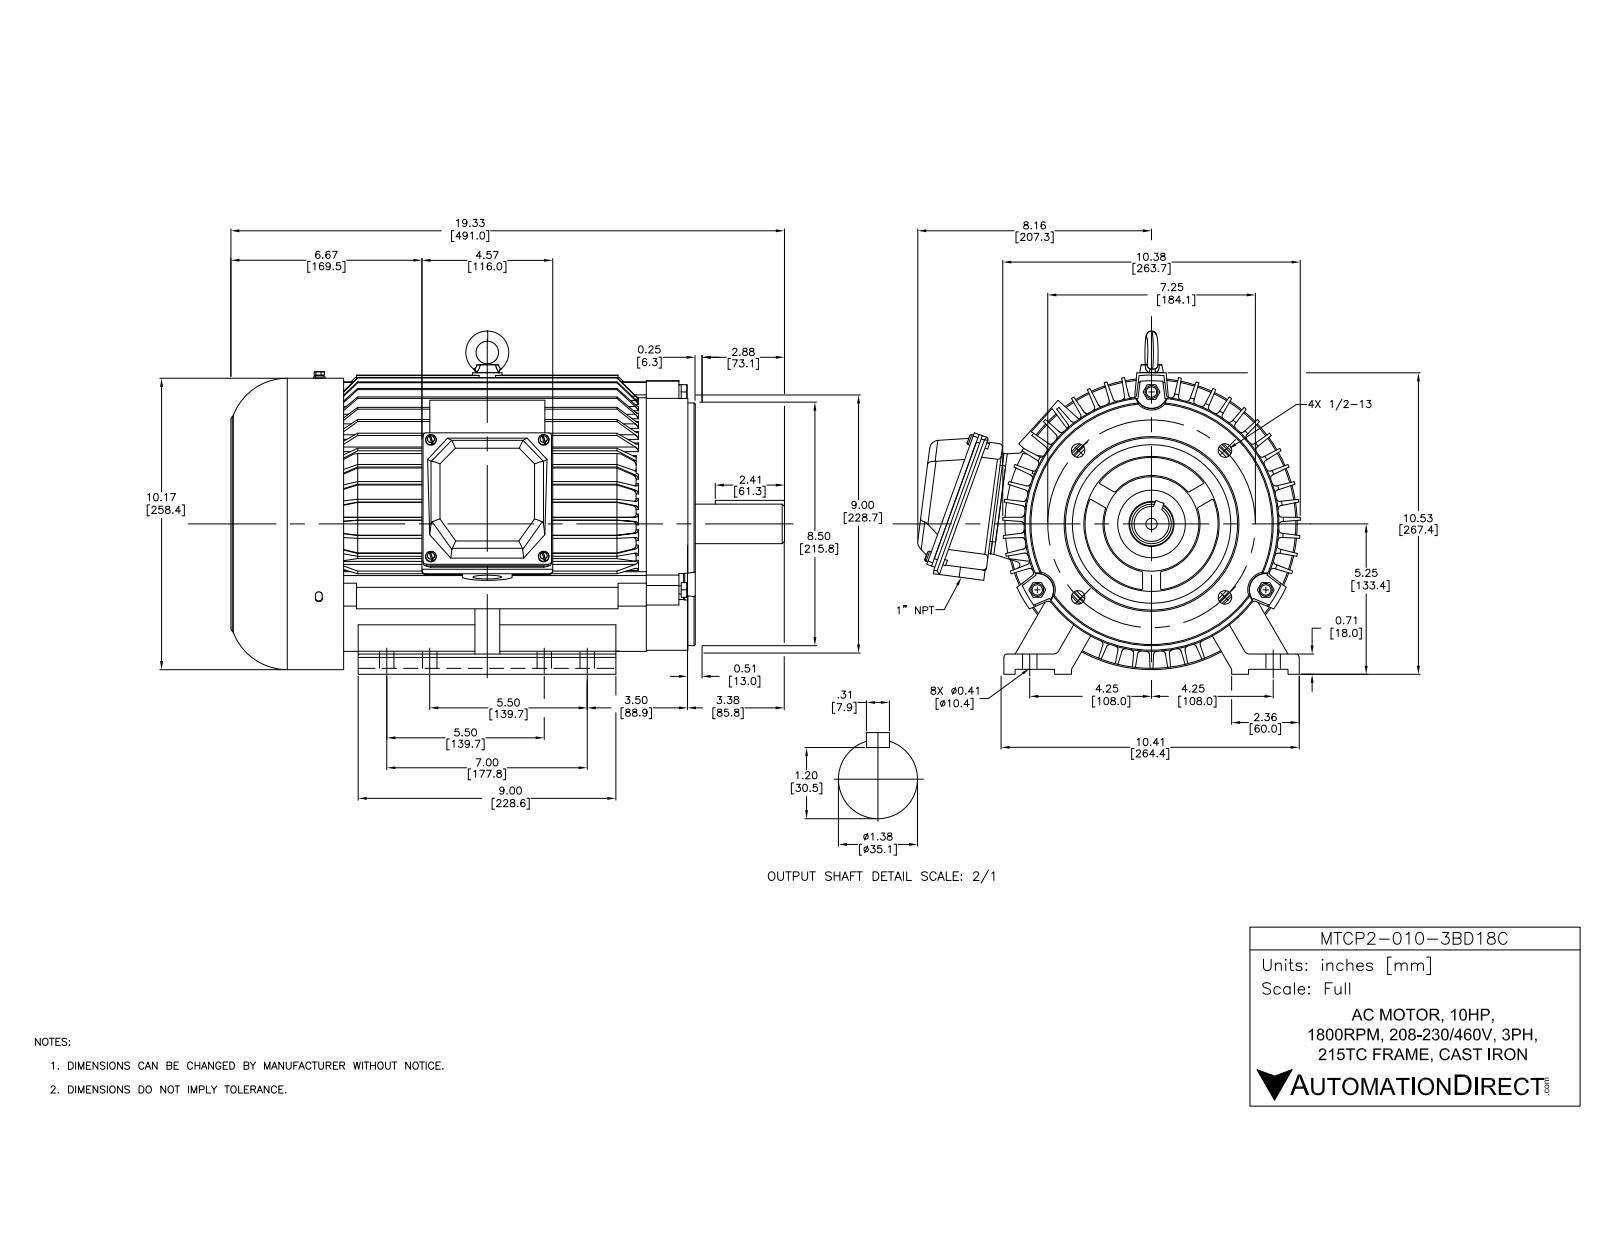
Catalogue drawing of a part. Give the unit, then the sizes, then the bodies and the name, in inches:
Units: inches
Overall size (bounding box): 19.331 × 13.36 × 11.986
Round holes (diameter × count): ⌀0.228 ×8, ⌀0.433 ×8, ⌀0.197 ×6, ⌀0.165 ×4, ⌀0.236 ×4, ⌀0.276 ×4, ⌀0.472 ×4, ⌀0.315 ×3, ⌀0.362 ×3, ⌀0.394 ×3, ⌀0.209 ×1, ⌀0.213 ×1
Round bosses / shafts (diameter × count): ⌀0.197 ×5, ⌀0.283 ×3, ⌀0.315 ×2, ⌀10.173 ×1, ⌀10.079 ×1, ⌀8.898 ×1, ⌀8.819 ×1, ⌀8.5 ×1
Partial cylindrical surfaces — rounded edges, fillets, slot ends (radius × count): R0.118 ×104, R0.039 ×12, R0.059 ×8, R0.157 ×8, R0.276 ×8, R0.315 ×8, R0.091 ×6, R0.433 ×6
Main face-to-face distances: 0.709, 0.157, 0.177, 0.531, 0.047, 16.108, 16.156, 0.642, 15.467, 15.514
Hole centre spacings: 3.937, 5.853, 4.331, 2.677, 1.5, 2.678, 3.785, 3.786
Volume: 279.1 in³ · Surface area: 2 120 in²
Bodies: 20 solids, 1781 faces (1036 planar, 506 cylindrical, 239 other)
Part name (STEP PRODUCT): PEWWE-215TC
STEP written by: SolidWorks 2017 (AUTOMOTIVE_DESIGN)
